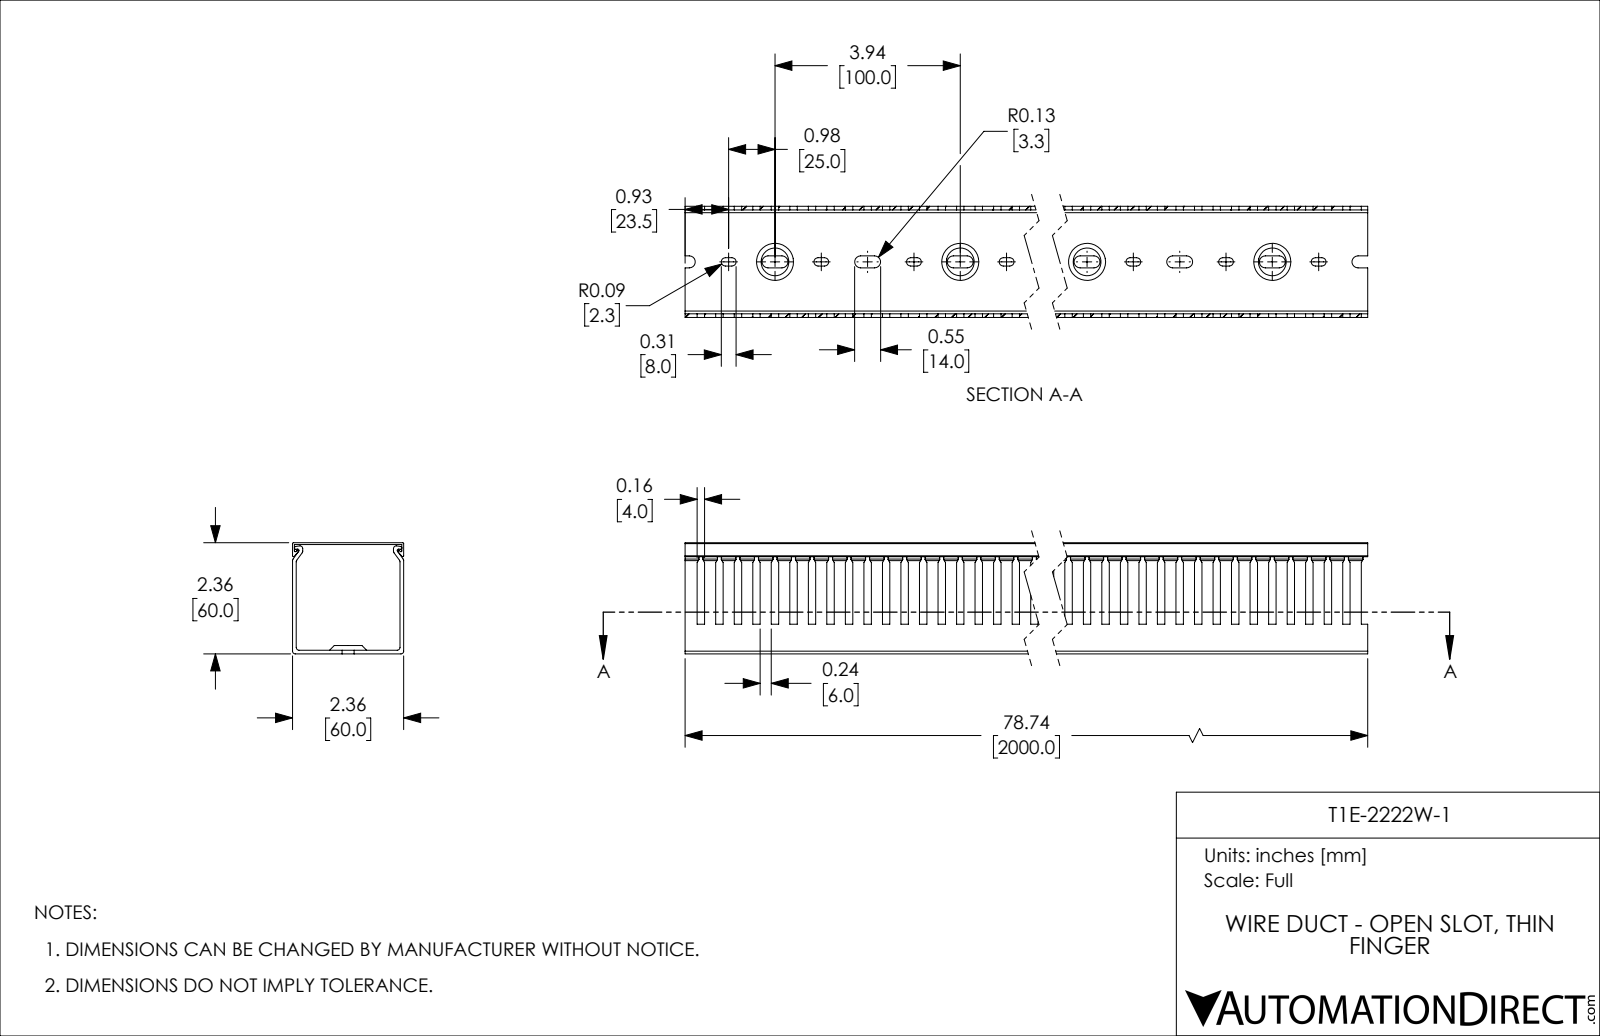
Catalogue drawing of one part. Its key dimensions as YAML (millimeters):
part_name: "T1E-2222W-1"
step_written_by: "SolidWorks 2021 (CONFIG_CONTROL_DESIGN)"
units: millimeters
bodies: {solids: 2, faces: 1005, planar: 534, cylindrical: 431, other: 40}
overall_size: [2000, 60, 60]
volume: 862740
surface_area: 1019000
partial_cylinders:
  - {radius: 2.25, count: 80}
  - {radius: 3.25, count: 80}
  - {radius: 1.5, count: 12}
  - {radius: 0.5, count: 8}
  - {radius: 0.75, count: 6}
face_to_face_distances: [2, 58, 60, 1, 59, 57, 56, 4.5, 54.5, 5.5]
